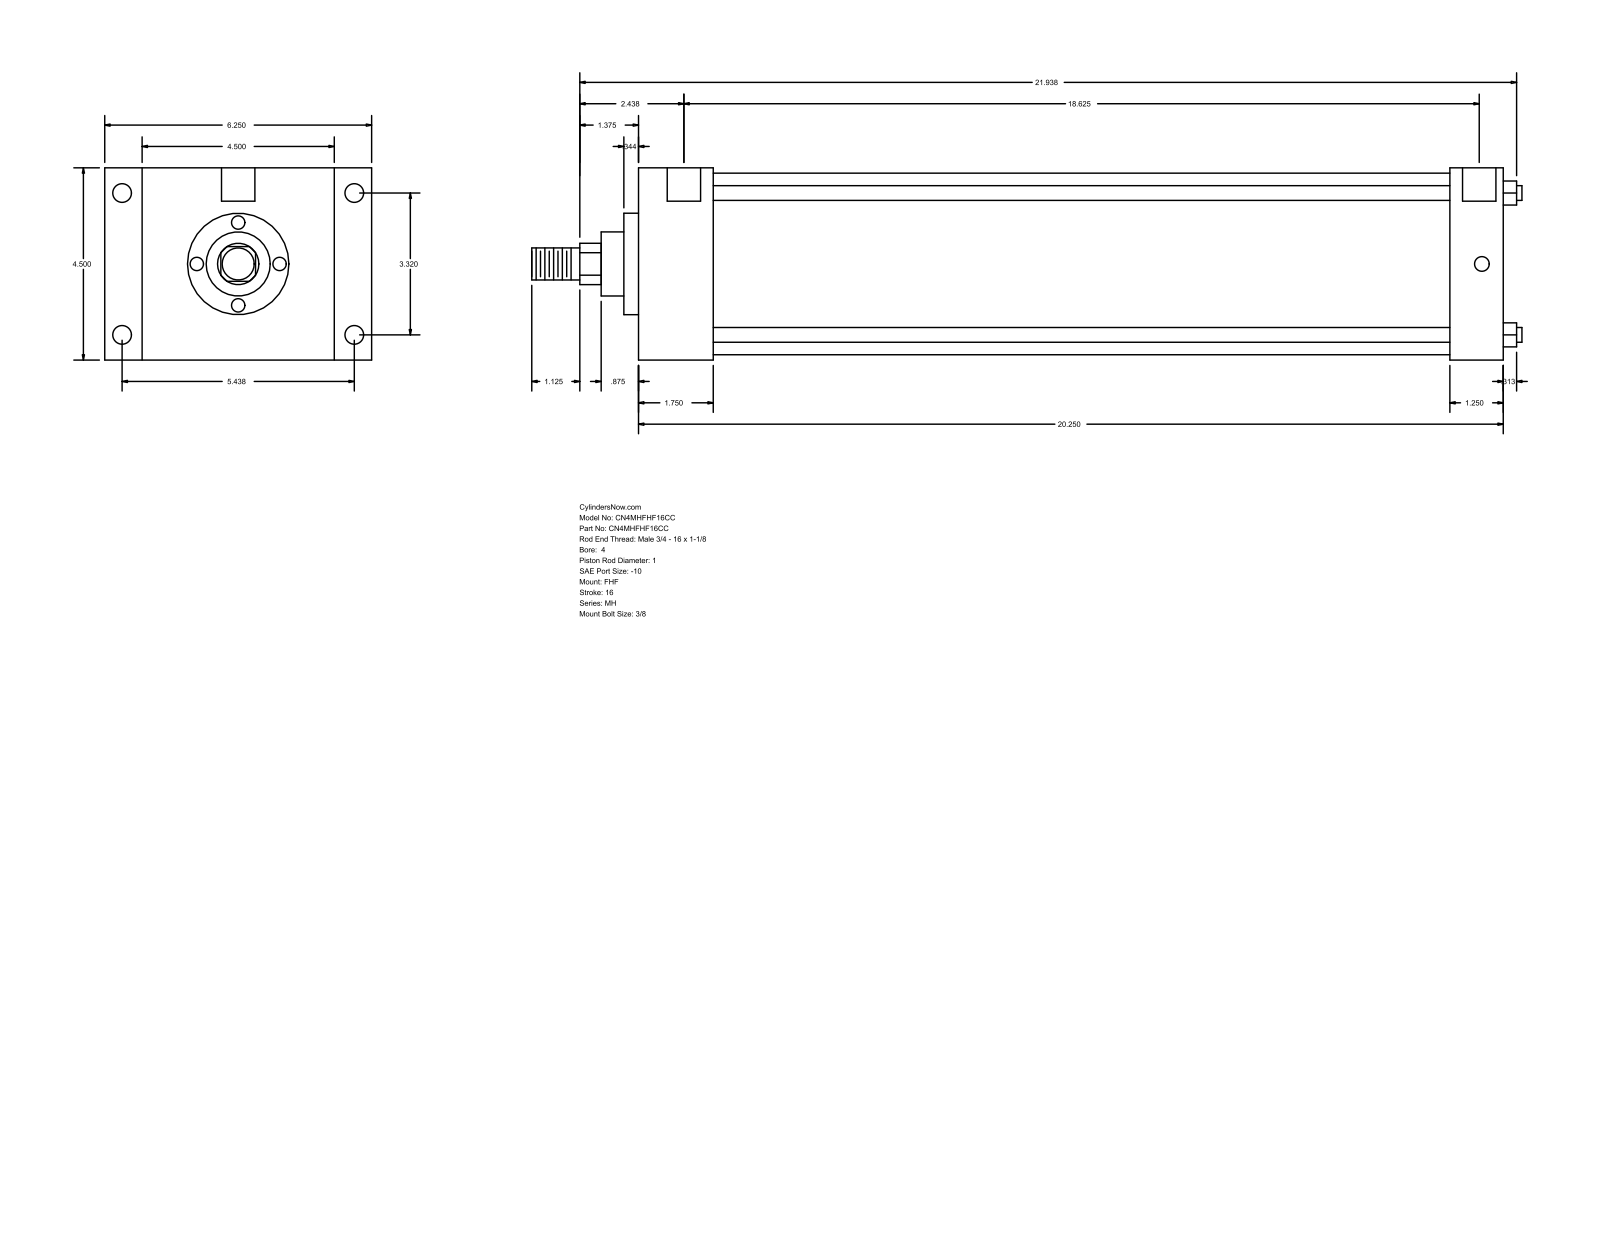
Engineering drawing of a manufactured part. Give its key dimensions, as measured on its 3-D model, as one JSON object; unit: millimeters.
{"part_name": "MH_FHF__0400_1", "step_written_by": "GSSL Pune (CONFIG_CONTROL_DESIGN)", "units": "millimeters", "bodies": {"solids": 0, "faces": 90, "planar": 61, "cylindrical": 29, "other": 0}, "overall_size": [588.96, 158.75, 114.3], "round_holes": [[8.73, 4], [11.13, 4], [19.84, 2]], "round_bosses_or_shafts": [[8.76, 4], [107.95, 1], [60.33, 1], [38.1, 1], [25.4, 1], [19.05, 1]], "partial_cylinders_radius": [[12.29, 1]], "face_to_face_distances": [114.3, 514.35, 44.46, 469.89, 22.23, 136.53, 158.76, 482.6, 438.14, 31.75], "hole_center_spacings": [84.32, 138.12, 161.82, 476.25, 1.58, 1.59, 473.08, 474.66]}
